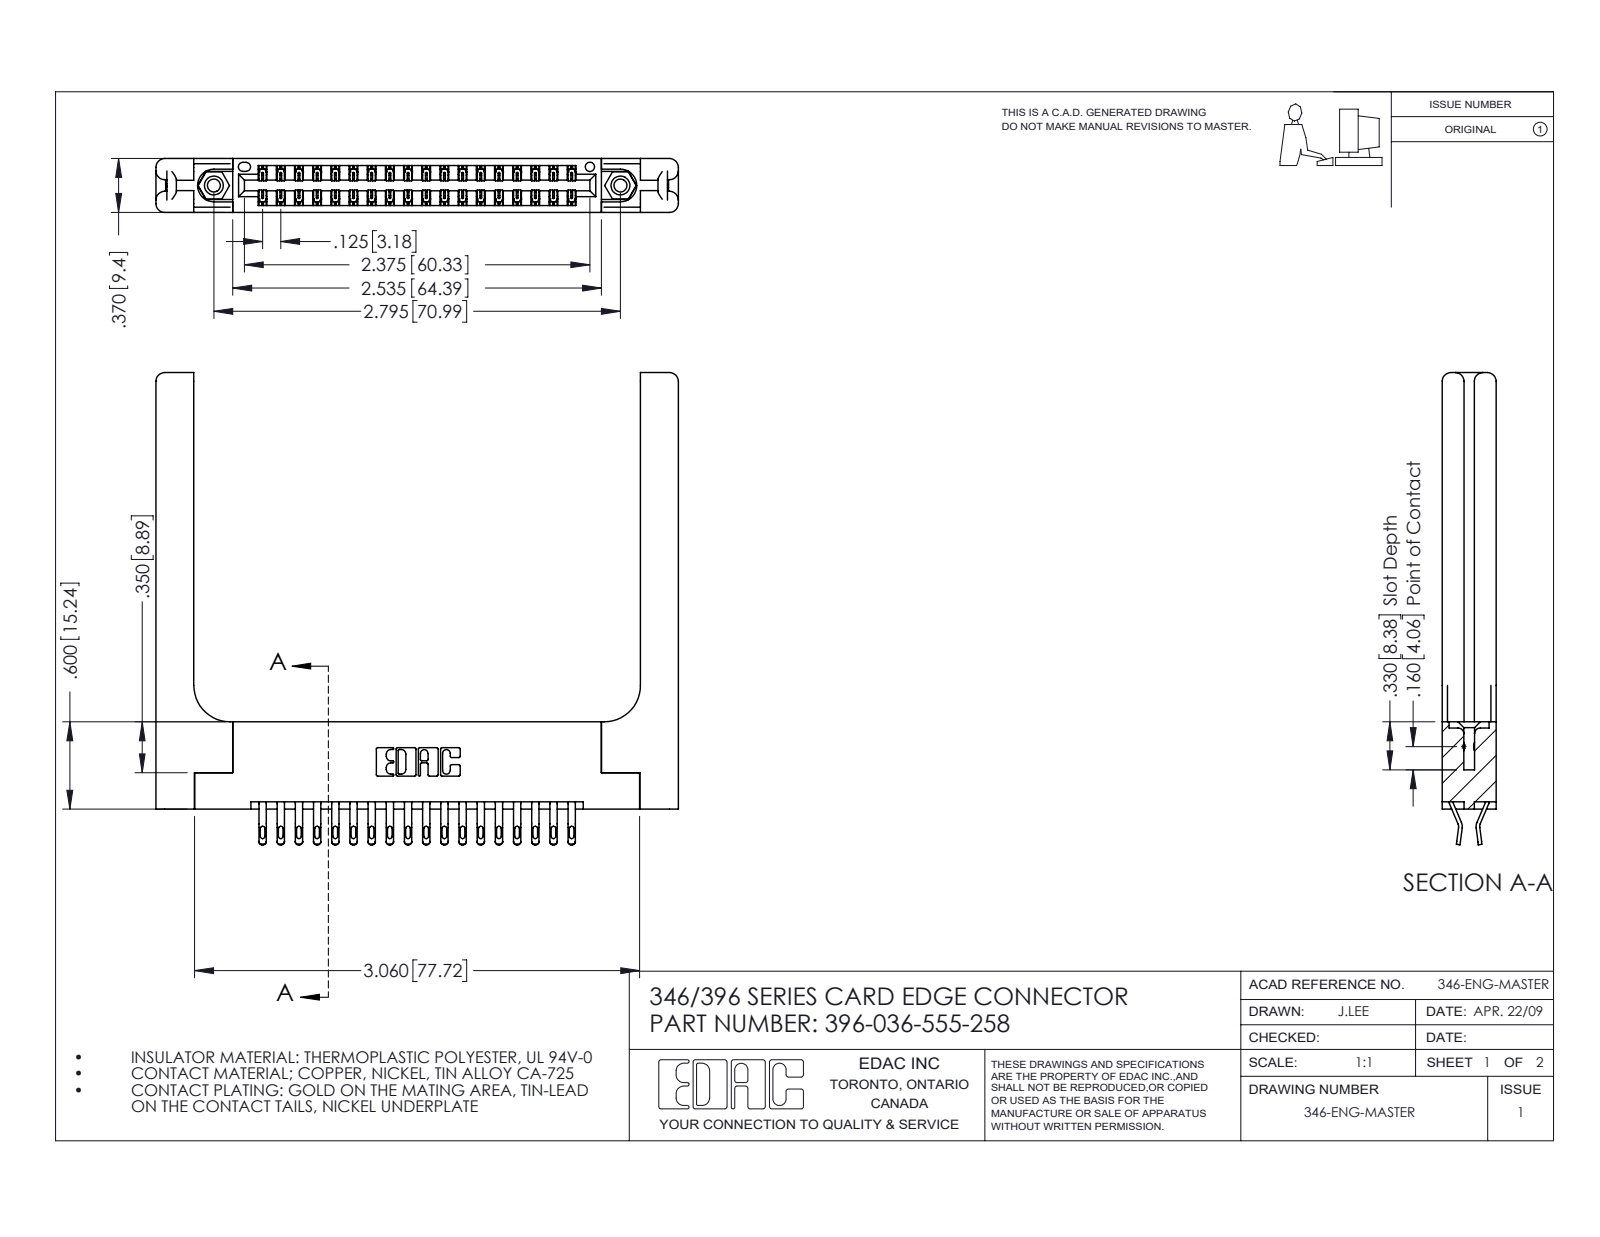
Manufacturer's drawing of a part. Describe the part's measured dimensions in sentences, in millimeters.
The part is named "345-292-001_555 Tail; 345-250-001_345-250-001-102; 396-036-555-258; 346 Part_Flush Mounting Lugs - 0.156 Dia-TH (+1 more)". Its 3-D file was written by "SolidWorks 2016 (CONFIG_CONTROL_DESIGN)". It is 41 solids with 2466 faces: 1412 planar, 994 cylindrical and 60 other. Overall it measures 91.2 by 82.4 by 9.4 millimeters. Its volume is 16 300 cubic millimeters and its surface area 17 080 square millimeters. Round holes: 2 of diameter 2.3, 2 of diameter 3.2, 2 of diameter 4, 1 of diameter 1.6. Round bosses or shafts: 2 of diameter 3.9. Partial cylindrical surfaces (rounded edges, fillets, slot ends): 72 of radius 0.4, 72 of radius 0.5, 54 of radius 0.2, 22 of radius 0.3, 16 of radius 1.5, 6 of radius 0.2, 6 of radius 0.8, 3 of radius 0.7. The main face-to-face distances are 9.4, 3.8, 1.8, 3.8, 1.2, 8.2, 6.4, 2.6, 5.6, 4.4. The hole center spacings are 6.2, 65.7, 71.
